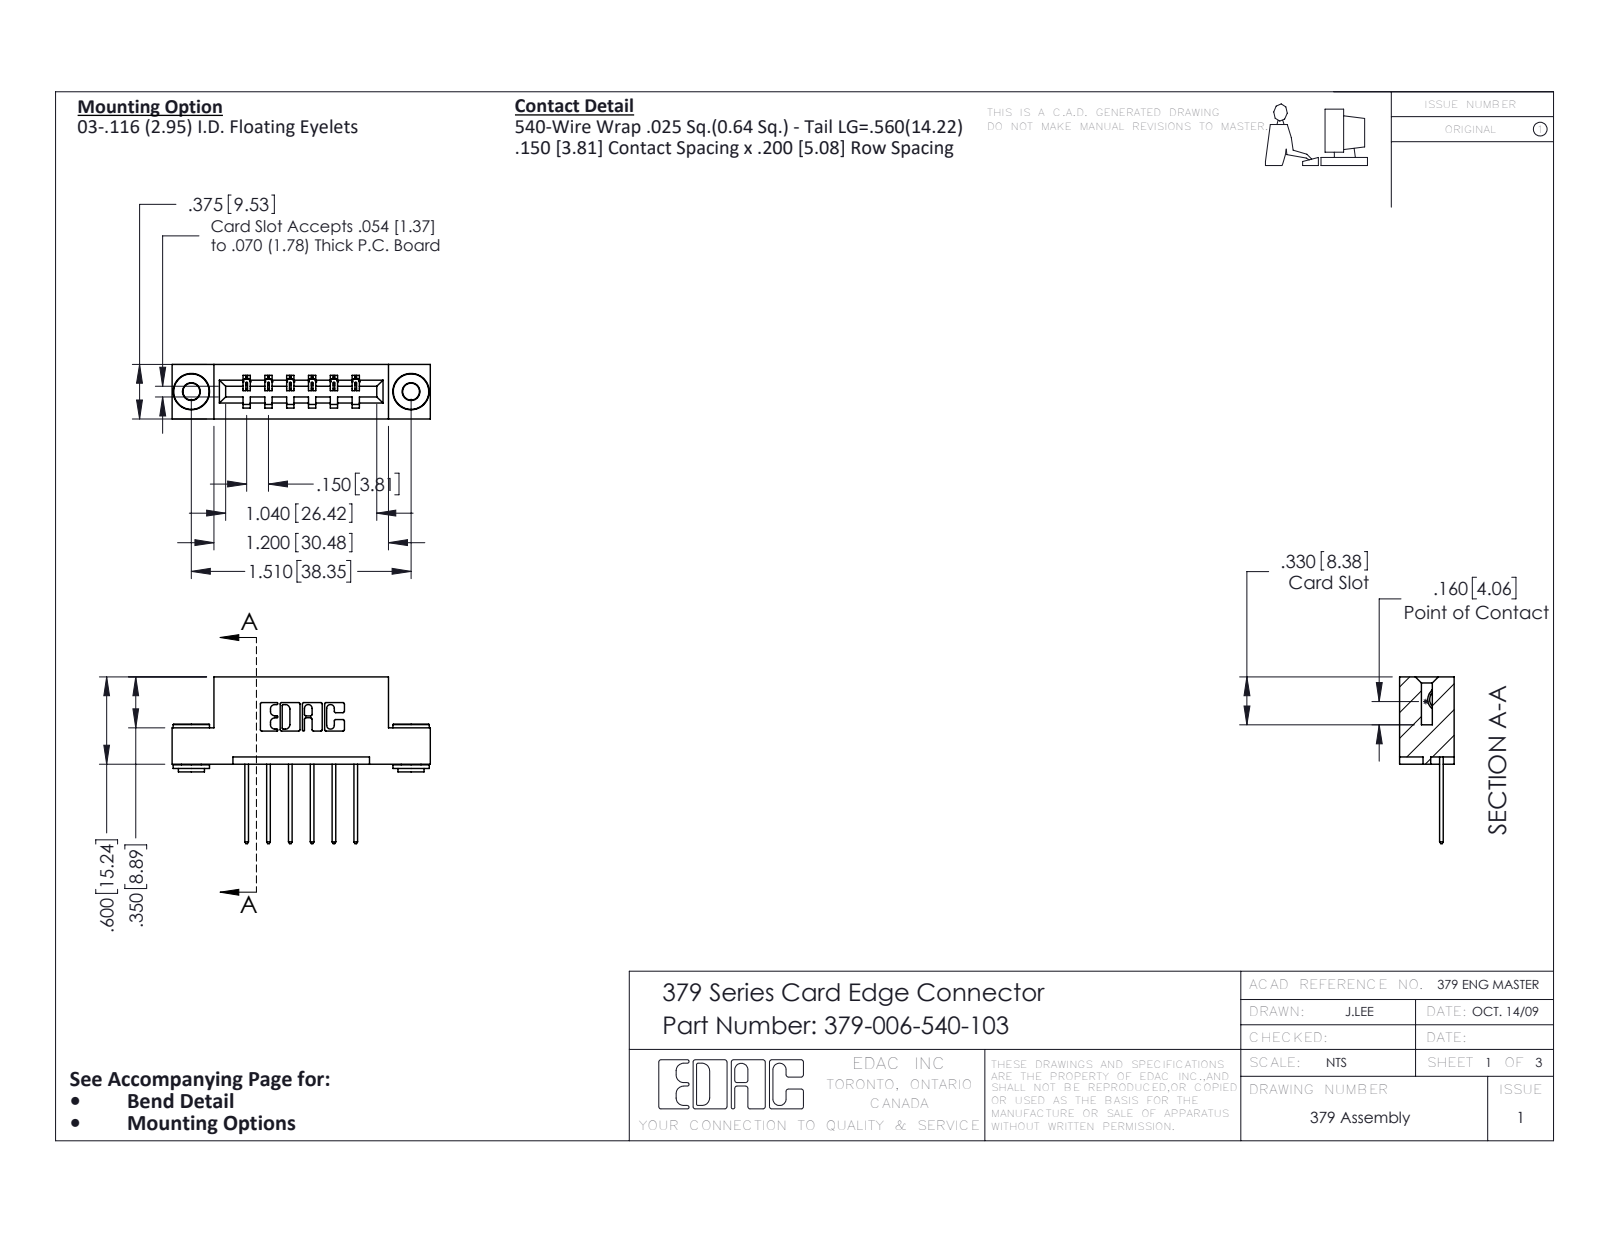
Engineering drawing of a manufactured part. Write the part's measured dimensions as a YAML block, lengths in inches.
part_name: "345-250-002_345-250-002-102; 379 Part_Flush - .156 Dia - TH; 345-292-001_345-293-140; 379-006-540-103"
step_written_by: "SolidWorks 2016 (CONFIG_CONTROL_DESIGN)"
units: inches
bodies: {solids: 9, faces: 500, planar: 332, cylindrical: 160, other: 8}
overall_size: [1.775, 1.147, 0.375]
volume: 0.265
surface_area: 7.052
round_holes:
  - {diameter: 0.116, count: 2}
  - {diameter: 0.156, count: 2}
round_bosses_or_shafts:
  - {diameter: 0.25, count: 2}
  - {diameter: 0.18, count: 2}
  - {diameter: 0.136, count: 2}
partial_cylinders:
  - {radius: 0.01, count: 22}
  - {radius: 0.006, count: 12}
  - {radius: 0.01, count: 12}
  - {radius: 0.007, count: 6}
  - {radius: 0.031, count: 6}
  - {radius: 0.026, count: 3}
  - {radius: 0.014, count: 1}
  - {radius: 0.022, count: 1}
face_to_face_distances: [0.3, 0.2, 0.375, 0.05, 0.15, 0.075, 0.25, 0.35, 0.1, 0.6]
hole_center_spacings: [1.51]
